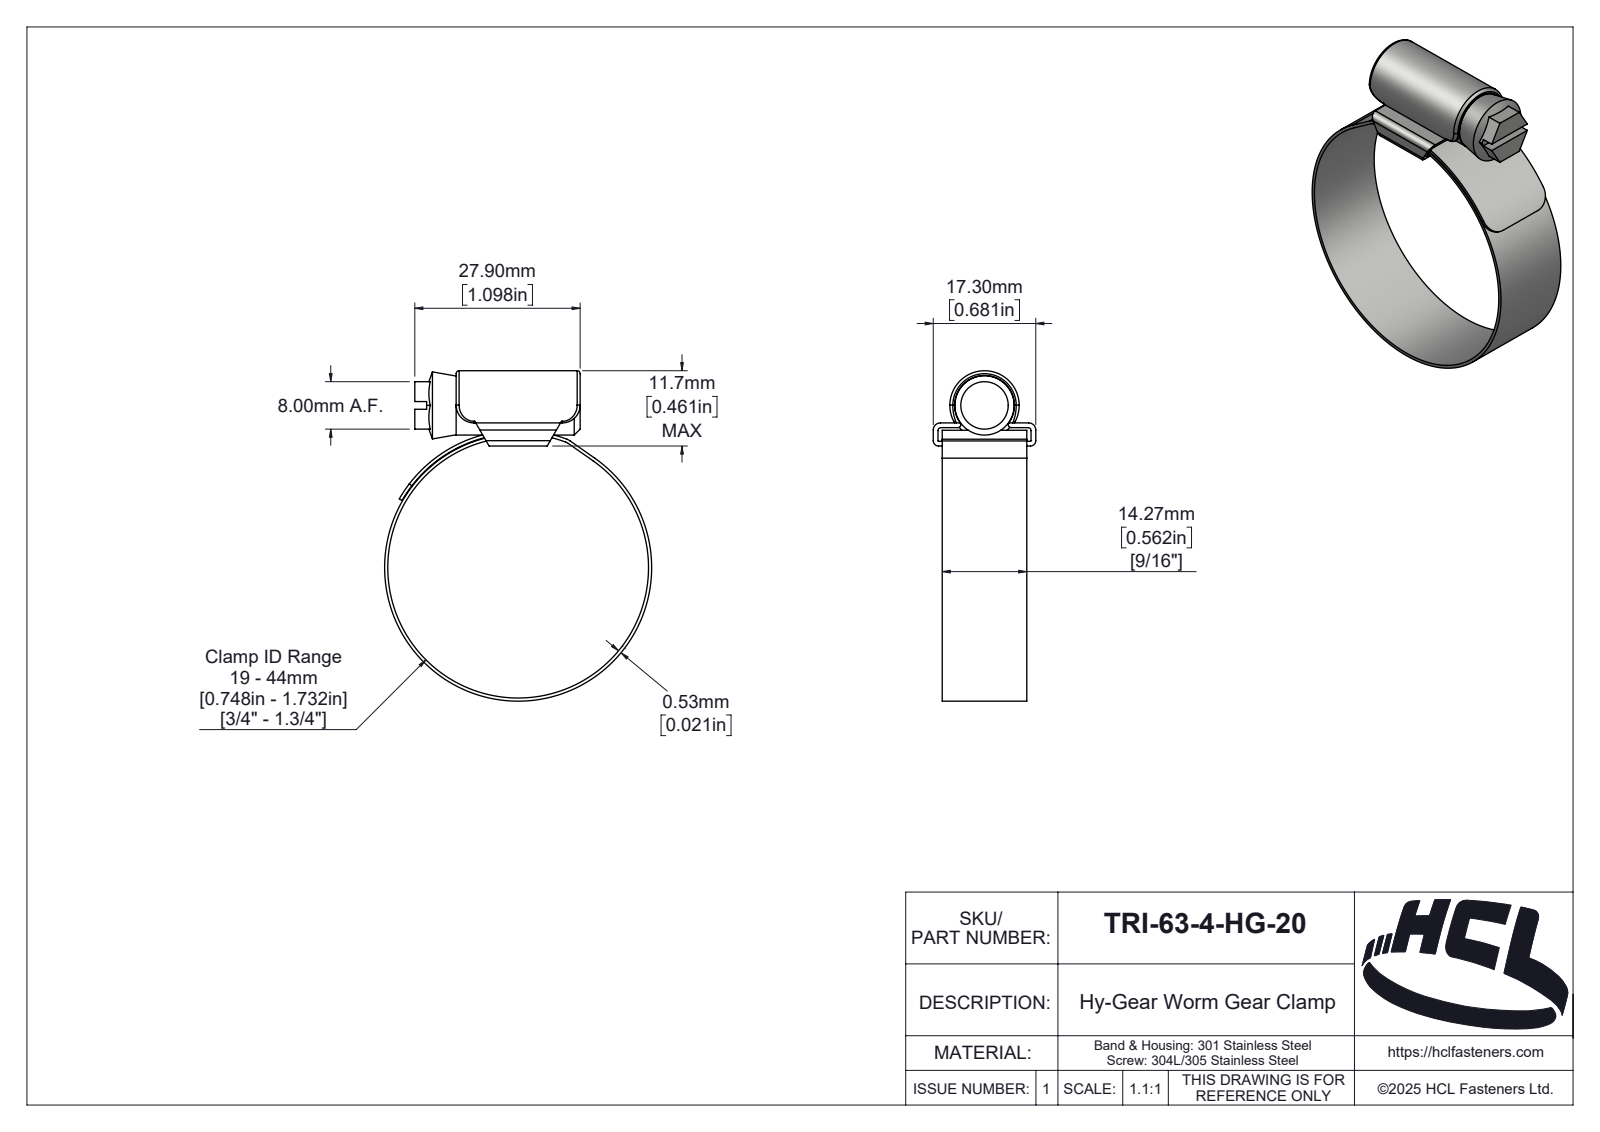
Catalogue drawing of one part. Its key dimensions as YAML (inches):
part_name: "TRI-50-0-HG-20"
step_written_by: "SolidWorks 2025 (AUTOMOTIVE_DESIGN)"
units: inches
bodies: {solids: 3, faces: 189, planar: 39, cylindrical: 89, other: 61}
overall_size: [2.194, 1.774, 0.681]
volume: 0.246
surface_area: 11.87
round_holes:
  - {diameter: 1.732, count: 1}
round_bosses_or_shafts:
  - {diameter: 1.774, count: 1}
  - {diameter: 0.394, count: 1}
partial_cylinders:
  - {radius: 0.02, count: 6}
  - {radius: 0.118, count: 4}
  - {radius: 0.004, count: 2}
  - {radius: 0.035, count: 2}
  - {radius: 0.047, count: 2}
  - {radius: 0.018, count: 1}
  - {radius: 0.074, count: 1}
  - {radius: 0.079, count: 1}
face_to_face_distances: [0.031, 0.122, 0.091, 0.561, 0.021, 0.154, 1.098, 0.06, 0.621, 0.65]
